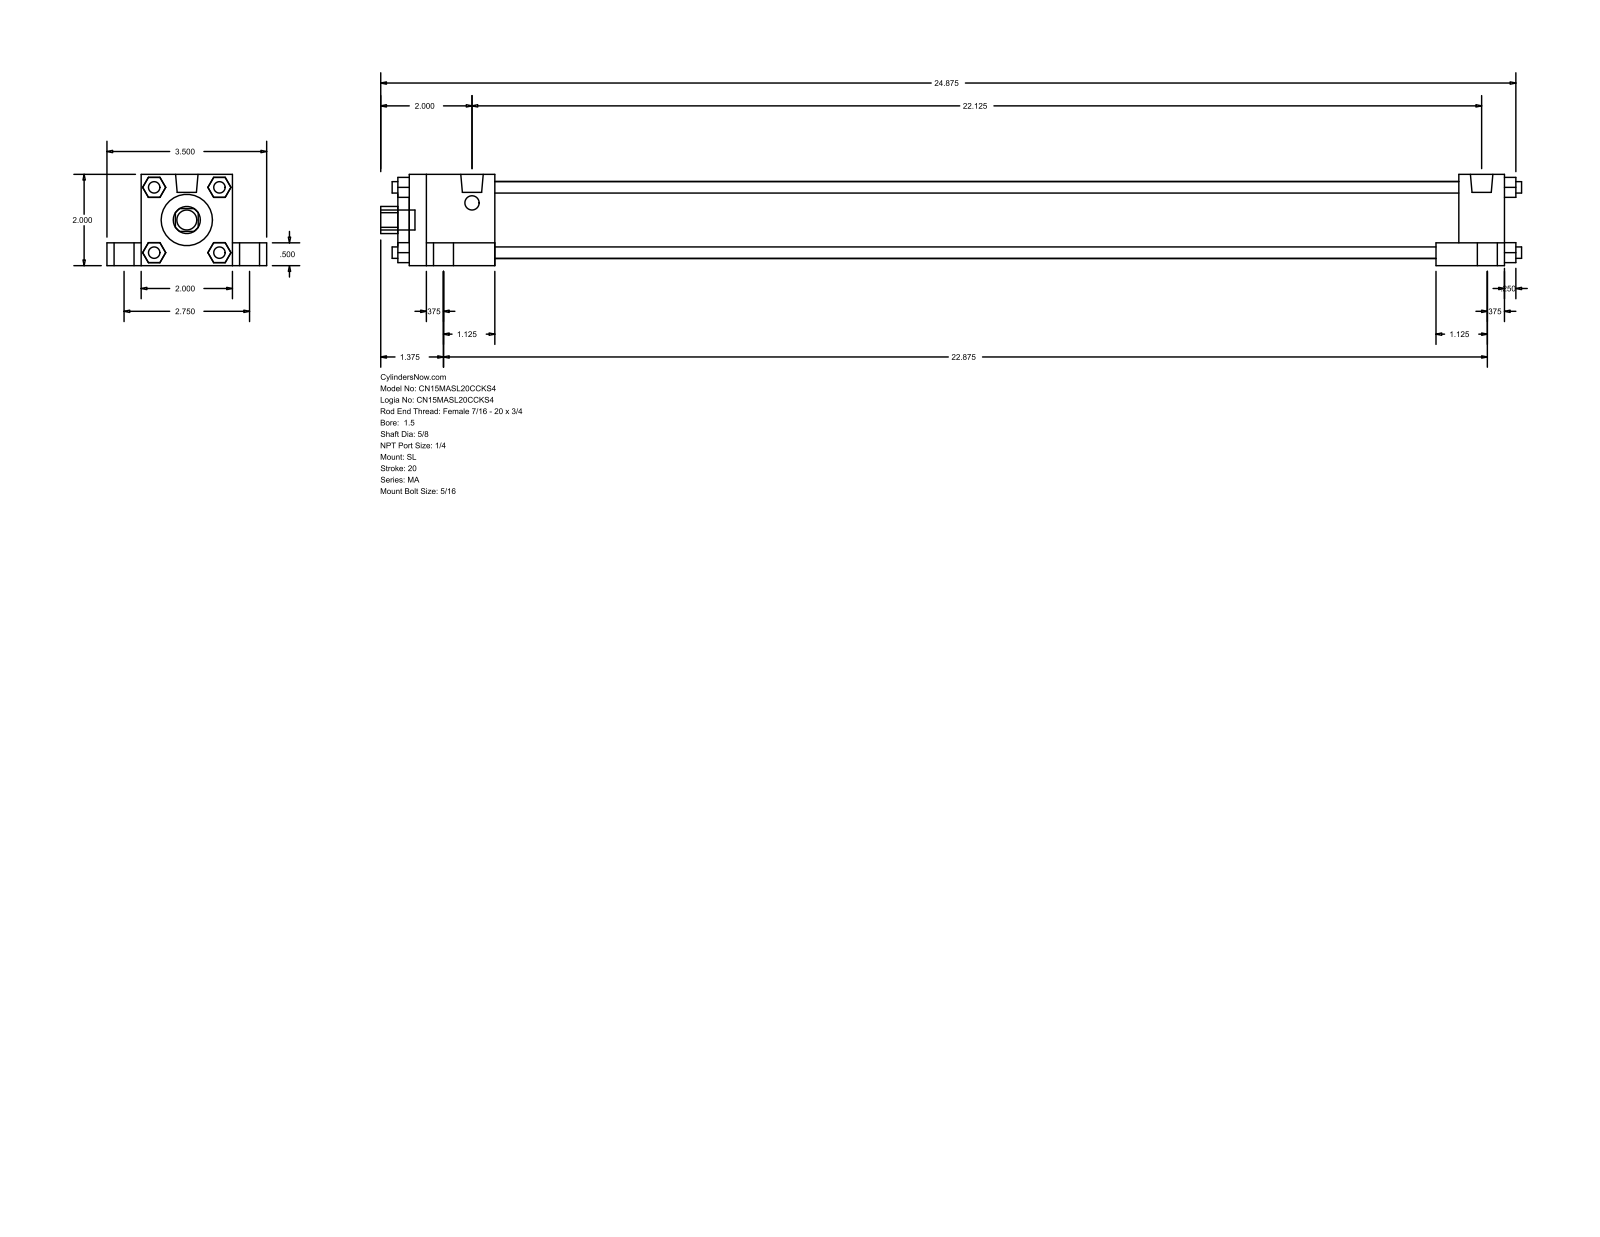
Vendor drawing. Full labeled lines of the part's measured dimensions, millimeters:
Part name (STEP PRODUCT): MA_SL__0150_0.625
STEP written by: GSSL Pune (CONFIG_CONTROL_DESIGN)
Units: millimetres
Bodies: 0 solids, 148 faces (112 planar, 36 cylindrical, 0 other)
Overall size (bounding box): 635 × 88.9 × 50.8
Round holes (diameter × count): ⌀15.88 ×1, ⌀28.57 ×1, ⌀42.93 ×1
Round bosses / shafts (diameter × count): ⌀11.11 ×5, ⌀17.46 ×4, ⌀7.94 ×4, ⌀6.35 ×4, ⌀12.49 ×2
Partial cylindrical surfaces — rounded edges, fillets, slot ends (radius × count): R7.54 ×1
Main face-to-face distances: 50.8, 19.05, 38.1, 12.7, 609.6, 69.85, 9.52, 6.35, 615.95, 25.4
